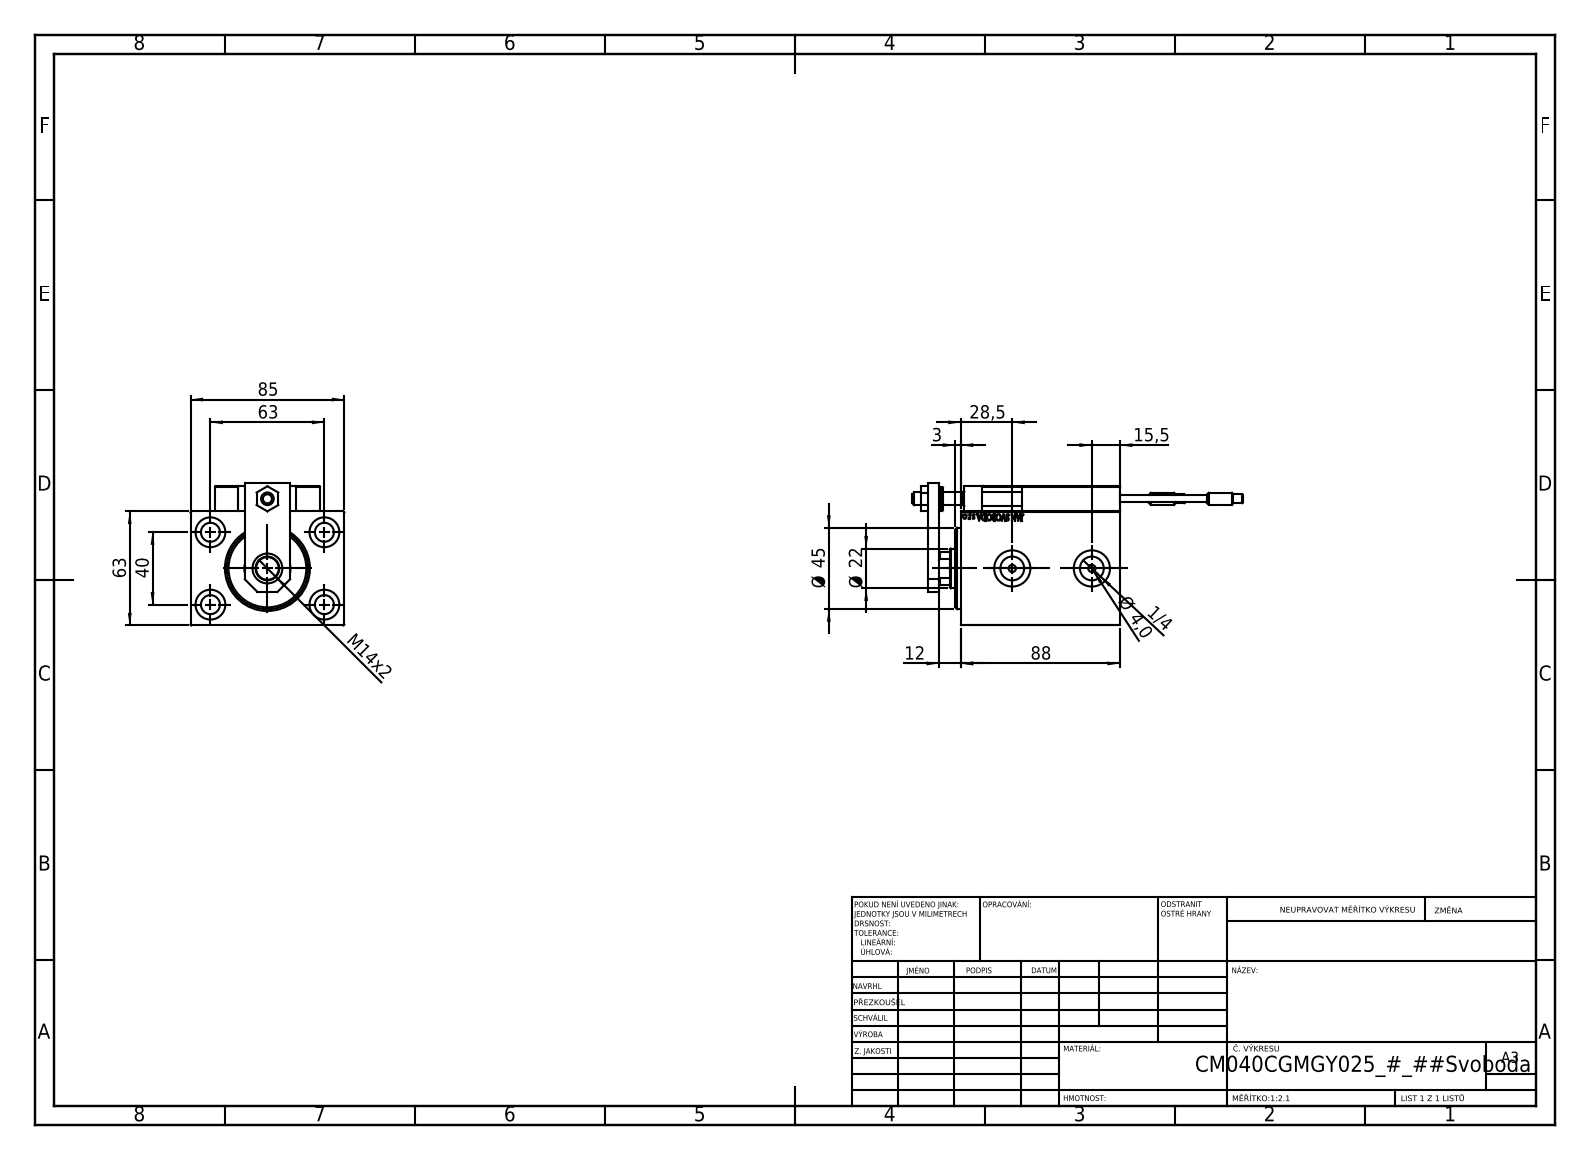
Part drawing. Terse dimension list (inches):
name: Block; SWITCH X; V450CM_C_VCP; SWITCH DIM B,W (+7 more)
written by: SolidWorks 2019 (CONFIG_CONTROL_DESIGN)
unit: in
bodies: 23 solids, 1304 faces (562 planar, 196 cylindrical, 546 other)
size: 7.193 × 3.346 × 3.091
volume: 27.98 in³; area: 159.1 in²
holes: 6× ⌀0.157, 5× ⌀0.315, 5× ⌀0.65, 4× ⌀0.126, 4× ⌀0.413, 2× ⌀0.197, 2× ⌀0.518, 2× ⌀0.787, 1× ⌀0.276, 1× ⌀0.492, 1× ⌀0.866, 1× ⌀1.004
bosses: 4× ⌀0.197, 2× ⌀0.256, 2× ⌀0.15, 1× ⌀0.512, 1× ⌀0.433
rounds: 30× R0.012, 2× R0.118, 1× R0.413
face distances: 2.48, 0.472, 3.346, 2.992, 3.465, 0.551, 3.031, 0.984, 0.591, 0.709
hole spacings: 1.469, 0.448, 0.787, 1.165, 1.169, 1.42, 1.438, 1.575
